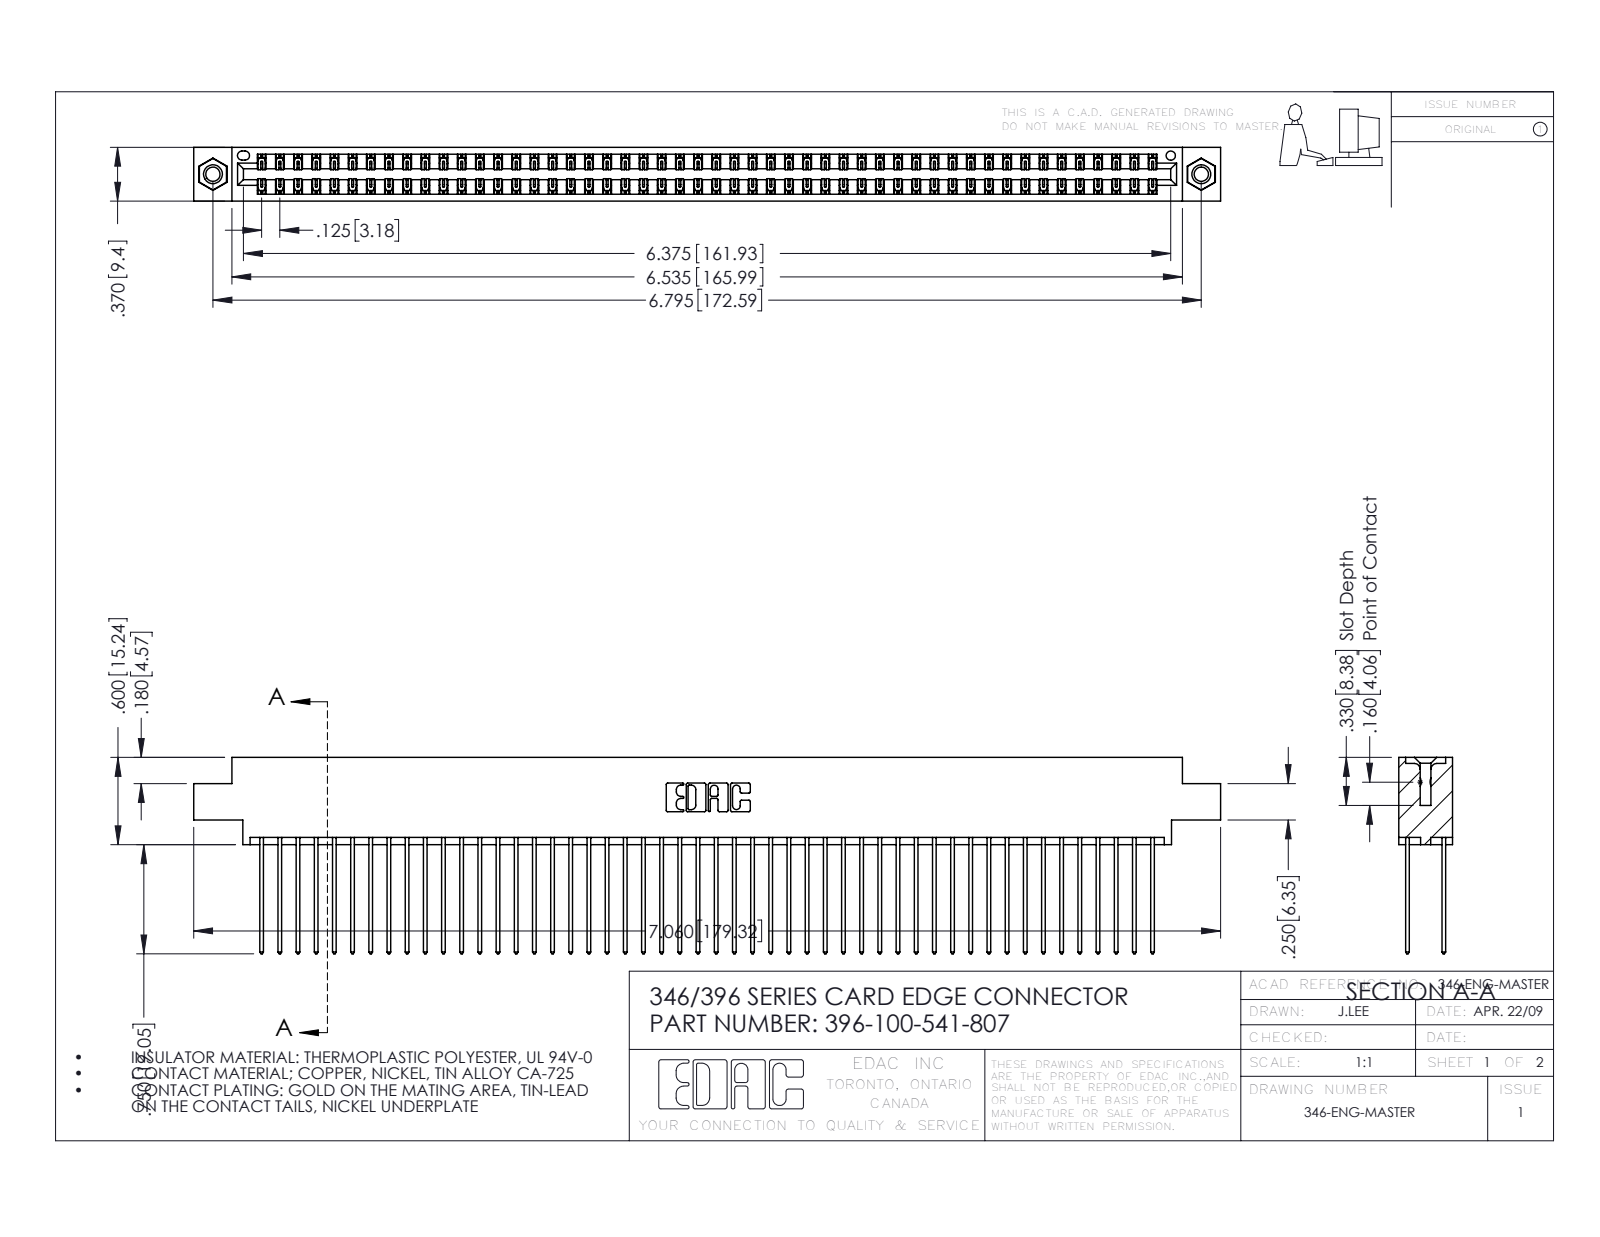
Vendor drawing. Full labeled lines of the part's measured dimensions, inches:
Part name (STEP PRODUCT): 345-292-001_345-293-141; 396-100-541-807; 346 Part_0.170 Offset - 0.156 Dia-TI; 345-250-001_345-250-005-103
STEP written by: SolidWorks 2016 (CONFIG_CONTROL_DESIGN)
Units: inches
Bodies: 103 solids, 5386 faces (3612 planar, 1758 cylindrical, 16 other)
Overall size (bounding box): 7.06 × 1.35 × 0.37
Volume: 1.096 in³ · Surface area: 43.04 in²
Round holes (diameter × count): ⌀0.098 ×2, ⌀0.125 ×2, ⌀0.156 ×2, ⌀0.064 ×1
Round bosses / shafts (diameter × count): ⌀0.155 ×2
Partial cylindrical surfaces — rounded edges, fillets, slot ends (radius × count): R0.006 ×150, R0.01 ×100, R0.01 ×22, R0.007 ×6, R0.031 ×6, R0.026 ×3, R0.014 ×2, R0.022 ×2
Main face-to-face distances: 0.048, 0.322, 0.25, 0.072, 0.298, 0.025, 0.37, 0.275, 0.225, 0.222
Hole centre spacings: 0.246, 6.586, 6.795
